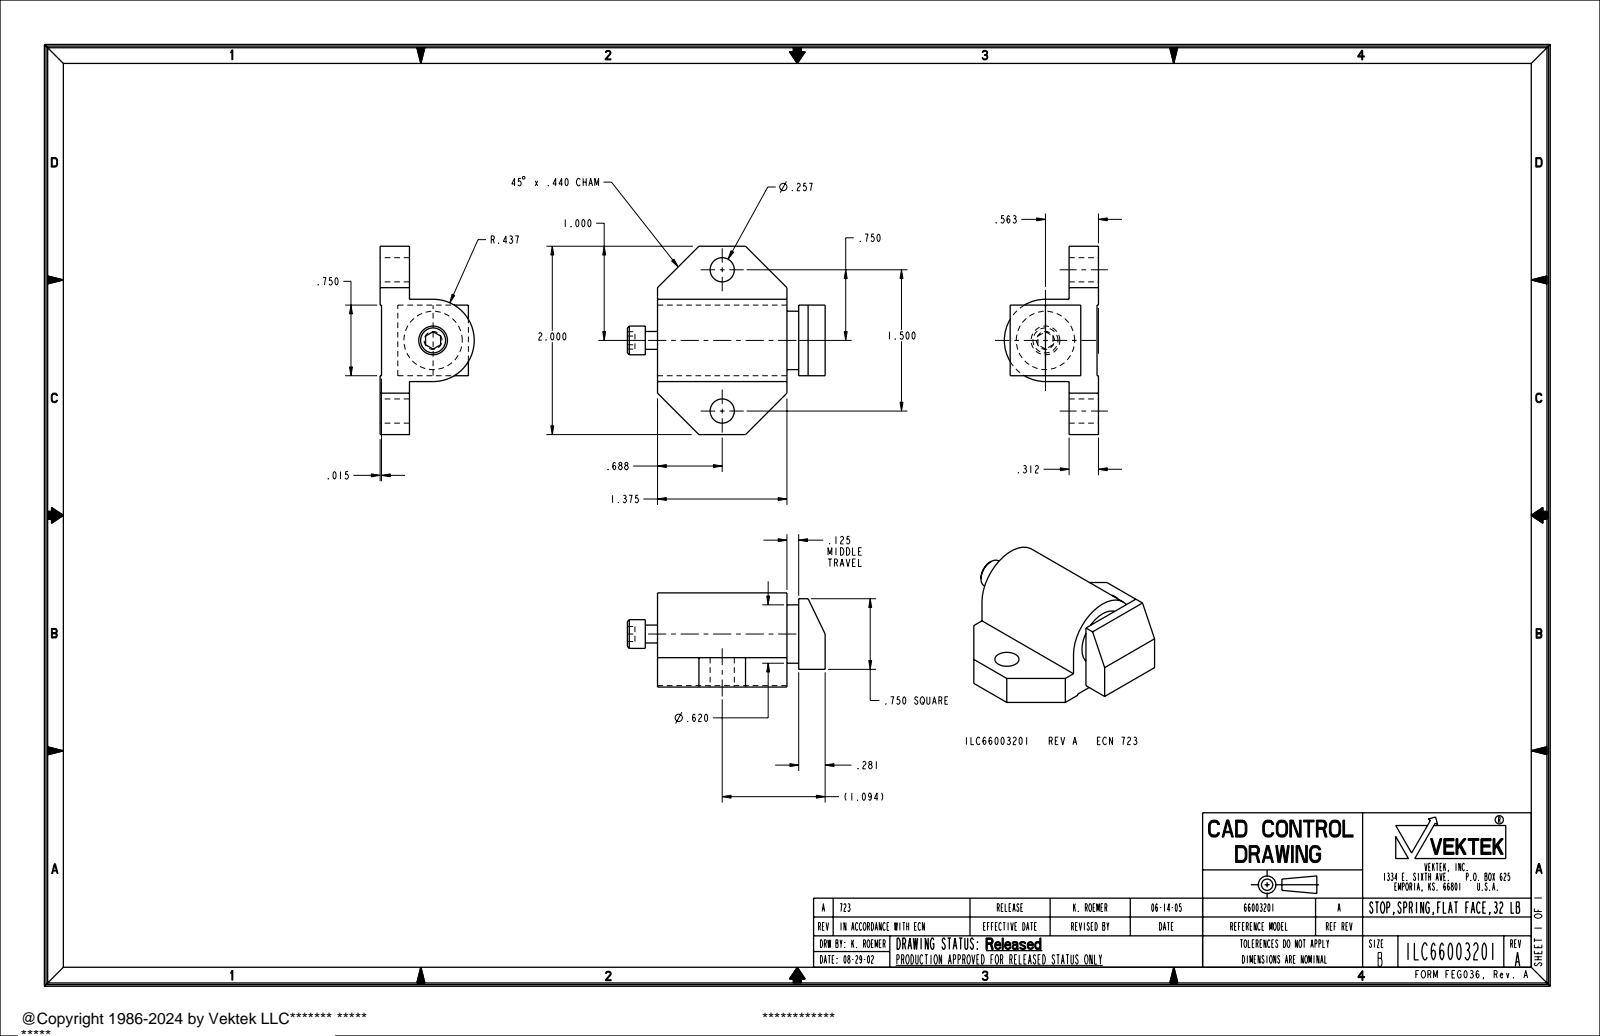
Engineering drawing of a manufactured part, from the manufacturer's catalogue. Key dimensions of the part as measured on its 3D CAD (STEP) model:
Part name (STEP PRODUCT): ILC66003201
STEP written by: PRO/ENGINEER BY PARAMETRIC TECHNOLOGY CORPORATION, 2004290 (AUTOMOTIVE_DESIGN_CC2)
Units: inches
Bodies: 1 solid, 46 faces (33 planar, 11 cylindrical, 2 other)
Overall size (bounding box): 2.101 × 2 × 1
Volume: 1.589 in³ · Surface area: 11.06 in²
Round holes (diameter × count): ⌀0.257 ×2
Round bosses / shafts (diameter × count): ⌀0.62 ×1, ⌀0.305 ×1, ⌀0.19 ×1
Partial cylindrical surfaces — rounded edges, fillets, slot ends (radius × count): R0.437 ×1
Main face-to-face distances: 0.312, 0.015, 0.297, 1.375, 0.062, 0.812, 1.764, 0.874, 0.563, 0.625
Hole centre spacings: 1.5
